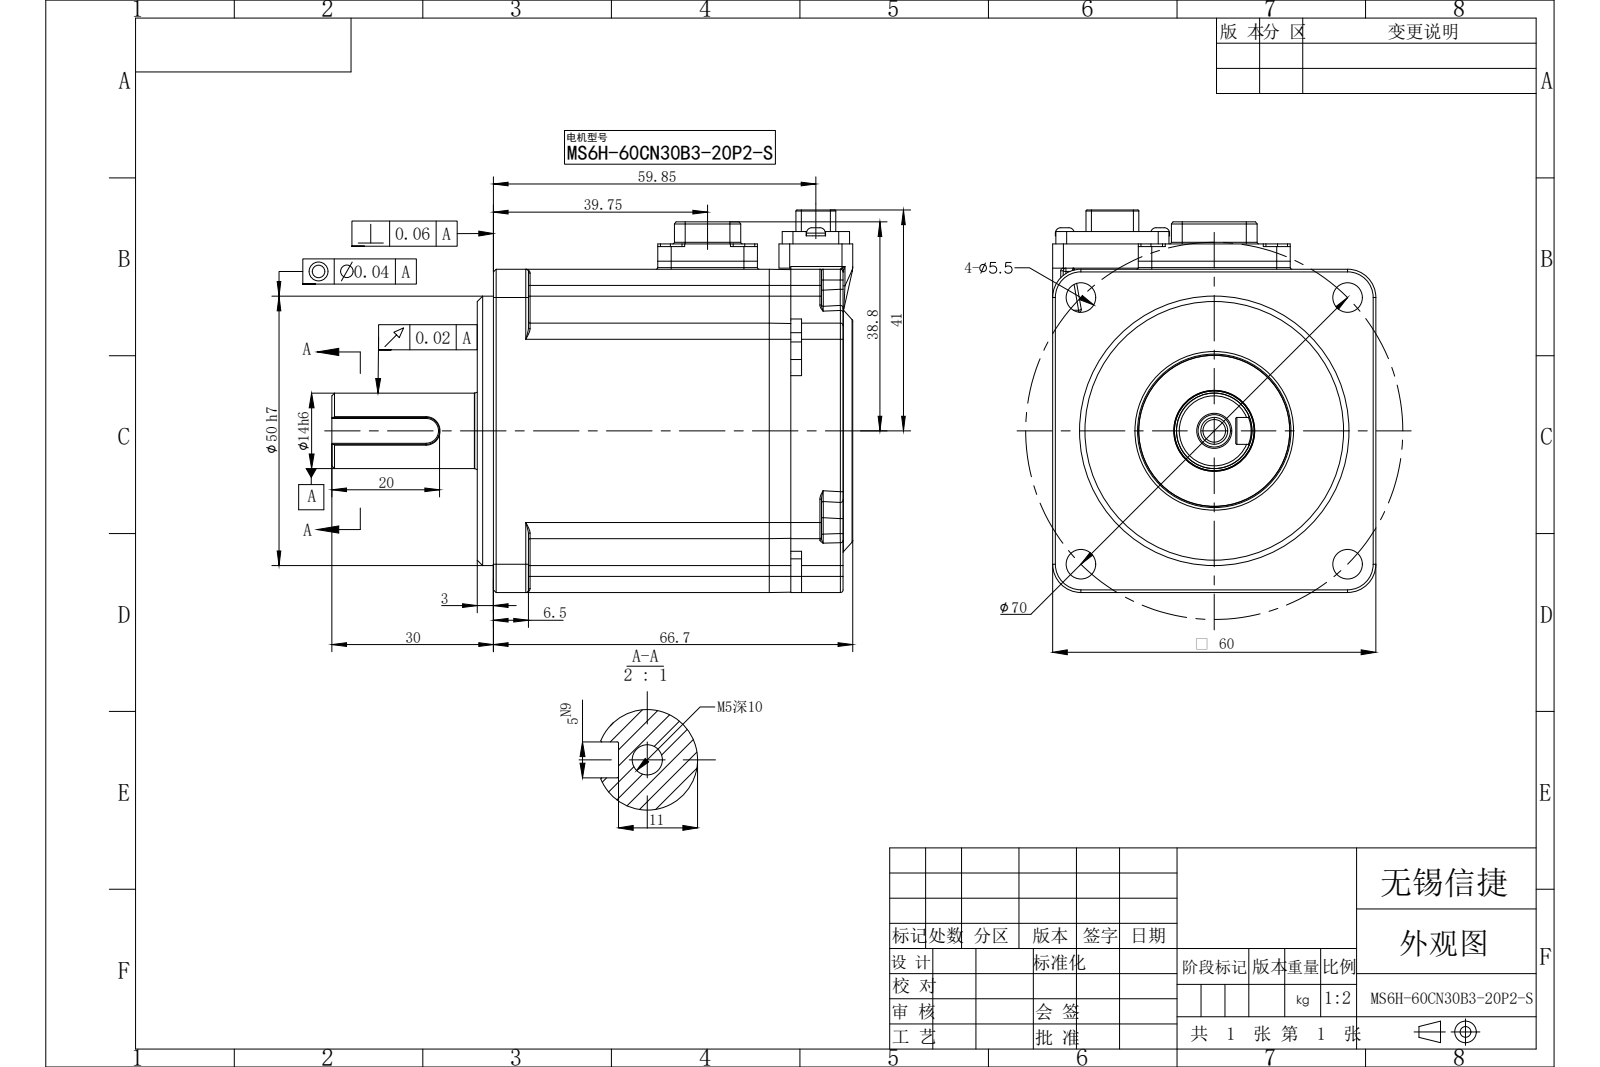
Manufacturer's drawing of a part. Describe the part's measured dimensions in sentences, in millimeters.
The part is named "MS6H-60CN30B3-20P2-S". Its 3-D file was written by "SolidWorks 2022 (CONFIG_CONTROL_DESIGN)". It is 0 solids with 731 faces: 301 planar, 252 cylindrical and 178 other. Overall it measures 96.7 by 71 by 60 millimeters. Round holes: 8 of diameter 2.1, 4 of diameter 3.4, 4 of diameter 5.5, 3 of diameter 3.5, 2 of diameter 1.6, 1 of diameter 4.2, 1 of diameter 5, 1 of diameter 15. Round bosses or shafts: 2 of diameter 3.5, 1 of diameter 50, 1 of diameter 28, 1 of diameter 14. Partial cylindrical surfaces (rounded edges, fillets, slot ends): 41 of radius 0.5, 38 of radius 0.3, 23 of radius 0.2, 17 of radius 3, 16 of radius 2, 5 of radius 1, 5 of radius 2.5, 4 of radius 0.6. The main face-to-face distances are 60, 11.5, 55.2, 66.7, 9.7, 1.8, 64.9, 69.7, 67.9, 58.2. The hole center spacings are 6.9, 8.43, 24.49, 31.22, 35, 41.29, 44.15, 49.5.
